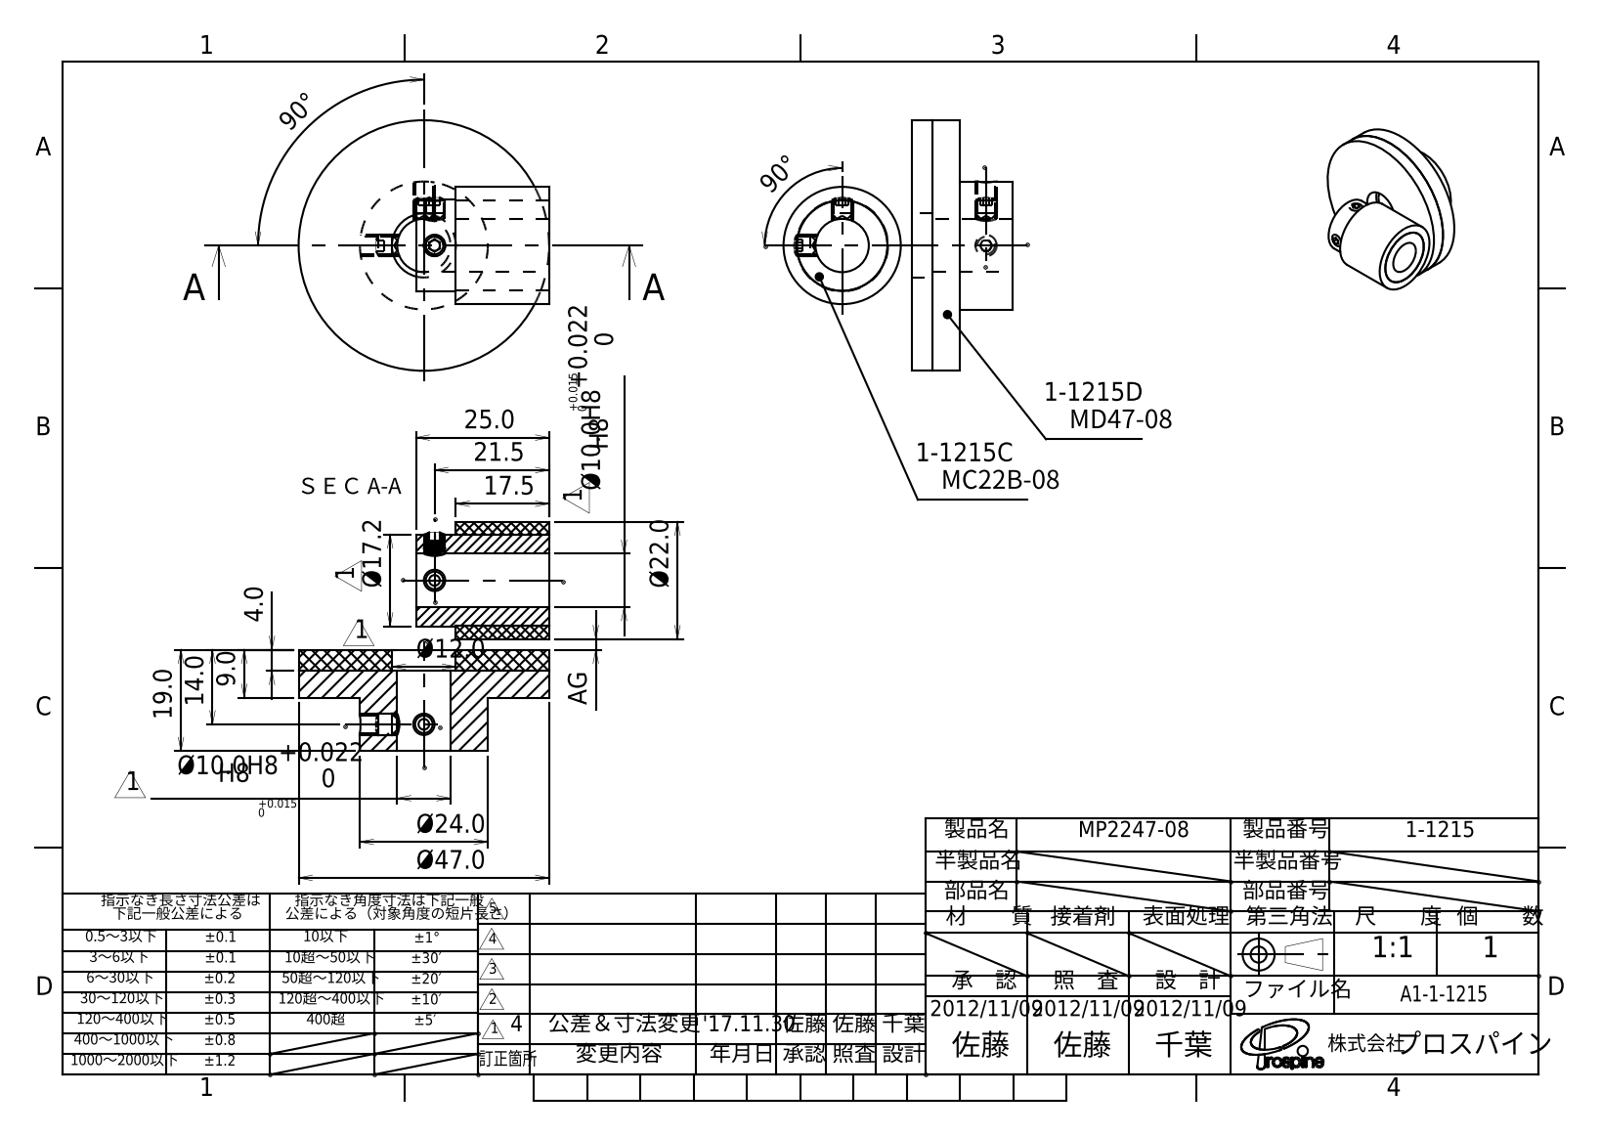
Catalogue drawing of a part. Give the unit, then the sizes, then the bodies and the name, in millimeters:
Units: millimetres
Overall size (bounding box): 47 × 47 × 43
Round holes (diameter × count): ⌀3.3 ×4, ⌀10 ×2, ⌀12 ×1, ⌀17 ×1
Round bosses / shafts (diameter × count): ⌀4 ×4, ⌀47 ×1, ⌀24 ×1, ⌀22 ×1, ⌀17.2 ×1
Main face-to-face distances: 4, 5, 9, 10, 15, 19, 17.5, 7.5, 25, 2
Hole centre spacings: 2, 27, 27.07
Volume: 25 050 mm³ · Surface area: 14 876 mm²
Bodies: 12 solids, 112 faces (66 planar, 22 cylindrical, 24 other)
STEP written by: PSStep 10.0 (CONFIG_CONTROL_DESIGN)
